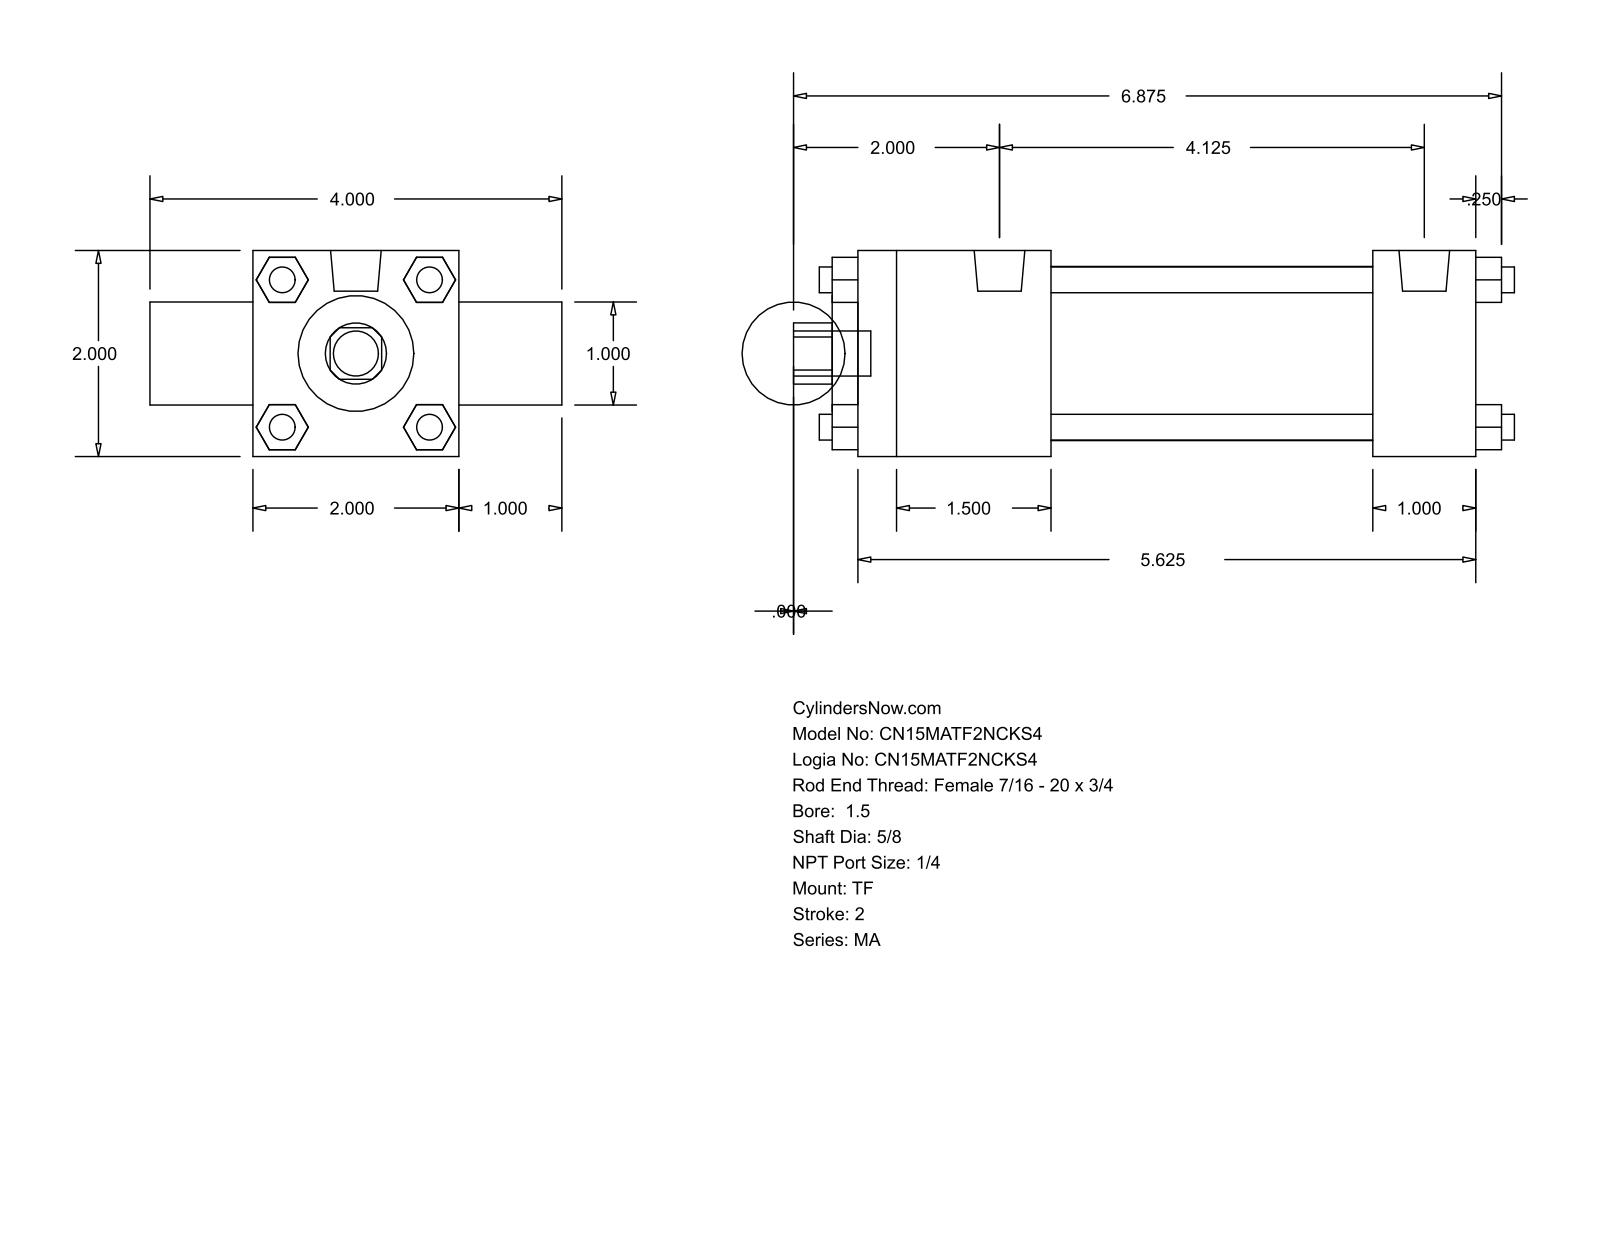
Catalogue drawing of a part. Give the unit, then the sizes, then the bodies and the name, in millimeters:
Units: millimetres
Overall size (bounding box): 177.8 × 101.6 × 50.8
Round holes (diameter × count): ⌀15.88 ×1, ⌀25.4 ×1, ⌀28.57 ×1, ⌀42.93 ×1
Round bosses / shafts (diameter × count): ⌀6.35 ×4, ⌀7.94 ×3, ⌀12.49 ×2, ⌀11.11 ×1
Partial cylindrical surfaces — rounded edges, fillets, slot ends (radius × count): R7.54 ×1
Main face-to-face distances: 50.8, 25.4, 152.4, 76.2, 47.62, 127, 79.38, 104.78, 158.75, 6.35
Bodies: 0 solids, 120 faces (92 planar, 28 cylindrical, 0 other)
Part name (STEP PRODUCT): MA_TF__0150_0.625
STEP written by: GSSL Pune (CONFIG_CONTROL_DESIGN)
